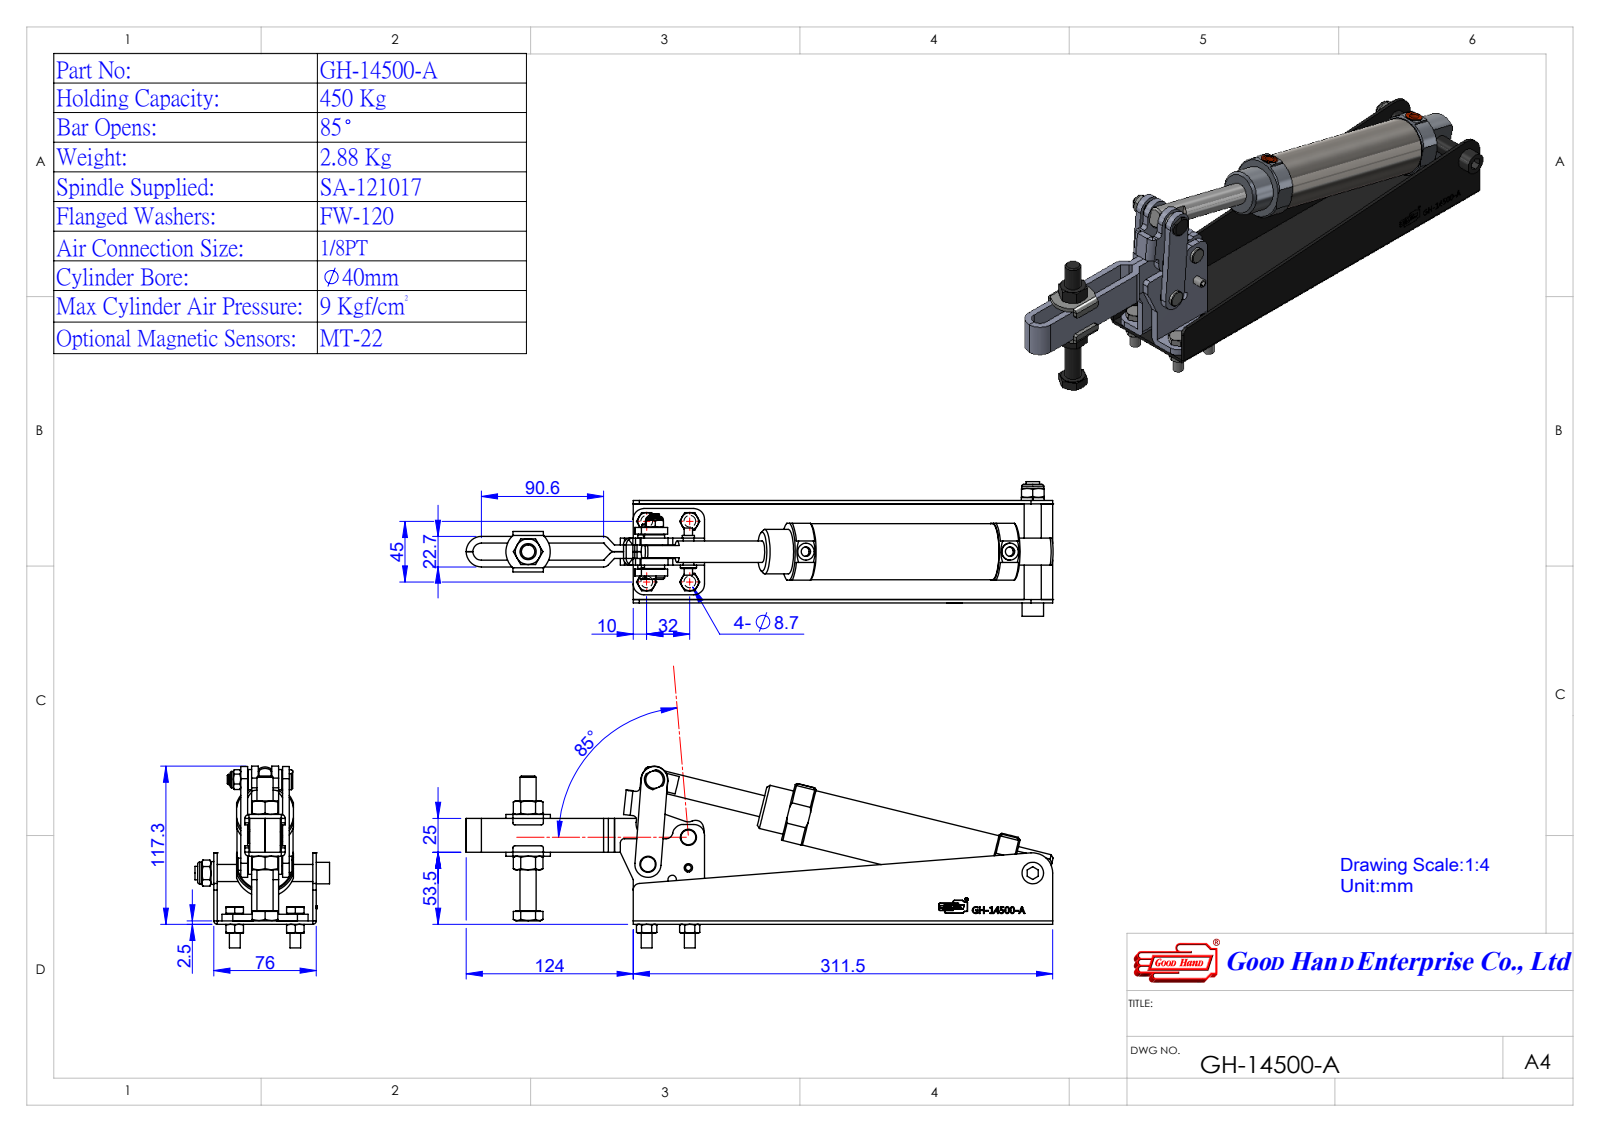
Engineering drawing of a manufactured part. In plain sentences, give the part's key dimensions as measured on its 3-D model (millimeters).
The part is named "Group7^GH-14500-A(簡化); Group5^GH-14500-A(簡化); GH-14500-A(簡化); Group2^GH-14500-A(簡化) (+4 more)". Its 3-D file was written by "SolidWorks 2016 (AUTOMOTIVE_DESIGN)". It is 7 solids with 641 faces: 281 planar, 228 cylindrical and 132 other. Overall it measures 436.26 by 135 by 97.92 millimeters. Its volume is 458 258 cubic millimeters and its surface area 238 603 square millimeters. Round holes: 4 of diameter 7, 2 of diameter 7.1, 2 of diameter 9.09, 2 of diameter 10.08, 2 of diameter 16, 1 of diameter 3.35, 1 of diameter 3.52, 1 of diameter 4.2, 1 of diameter 6, 1 of diameter 10.56, 1 of diameter 12.7, 1 of diameter 40. Round bosses or shafts: 4 of diameter 12, 4 of diameter 11.63, 4 of diameter 8, 2 of diameter 16, 2 of diameter 12.6, 2 of diameter 8.95, 1 of diameter 41.65, 1 of diameter 38. Partial cylindrical surfaces (rounded edges, fillets, slot ends): 6 of radius 5.01, 6 of radius 8, 4 of radius 1.5, 4 of radius 3.01, 2 of radius 2.51, 2 of radius 3, 2 of radius 5, 2 of radius 6. The main face-to-face distances are 2.5, 73.5, 5, 71, 76, 28, 43, 40.5, 33, 30.5. The hole center spacings are 14.76, 21.2, 22.6, 30.04, 30.11, 30.54, 33, 33.43.
